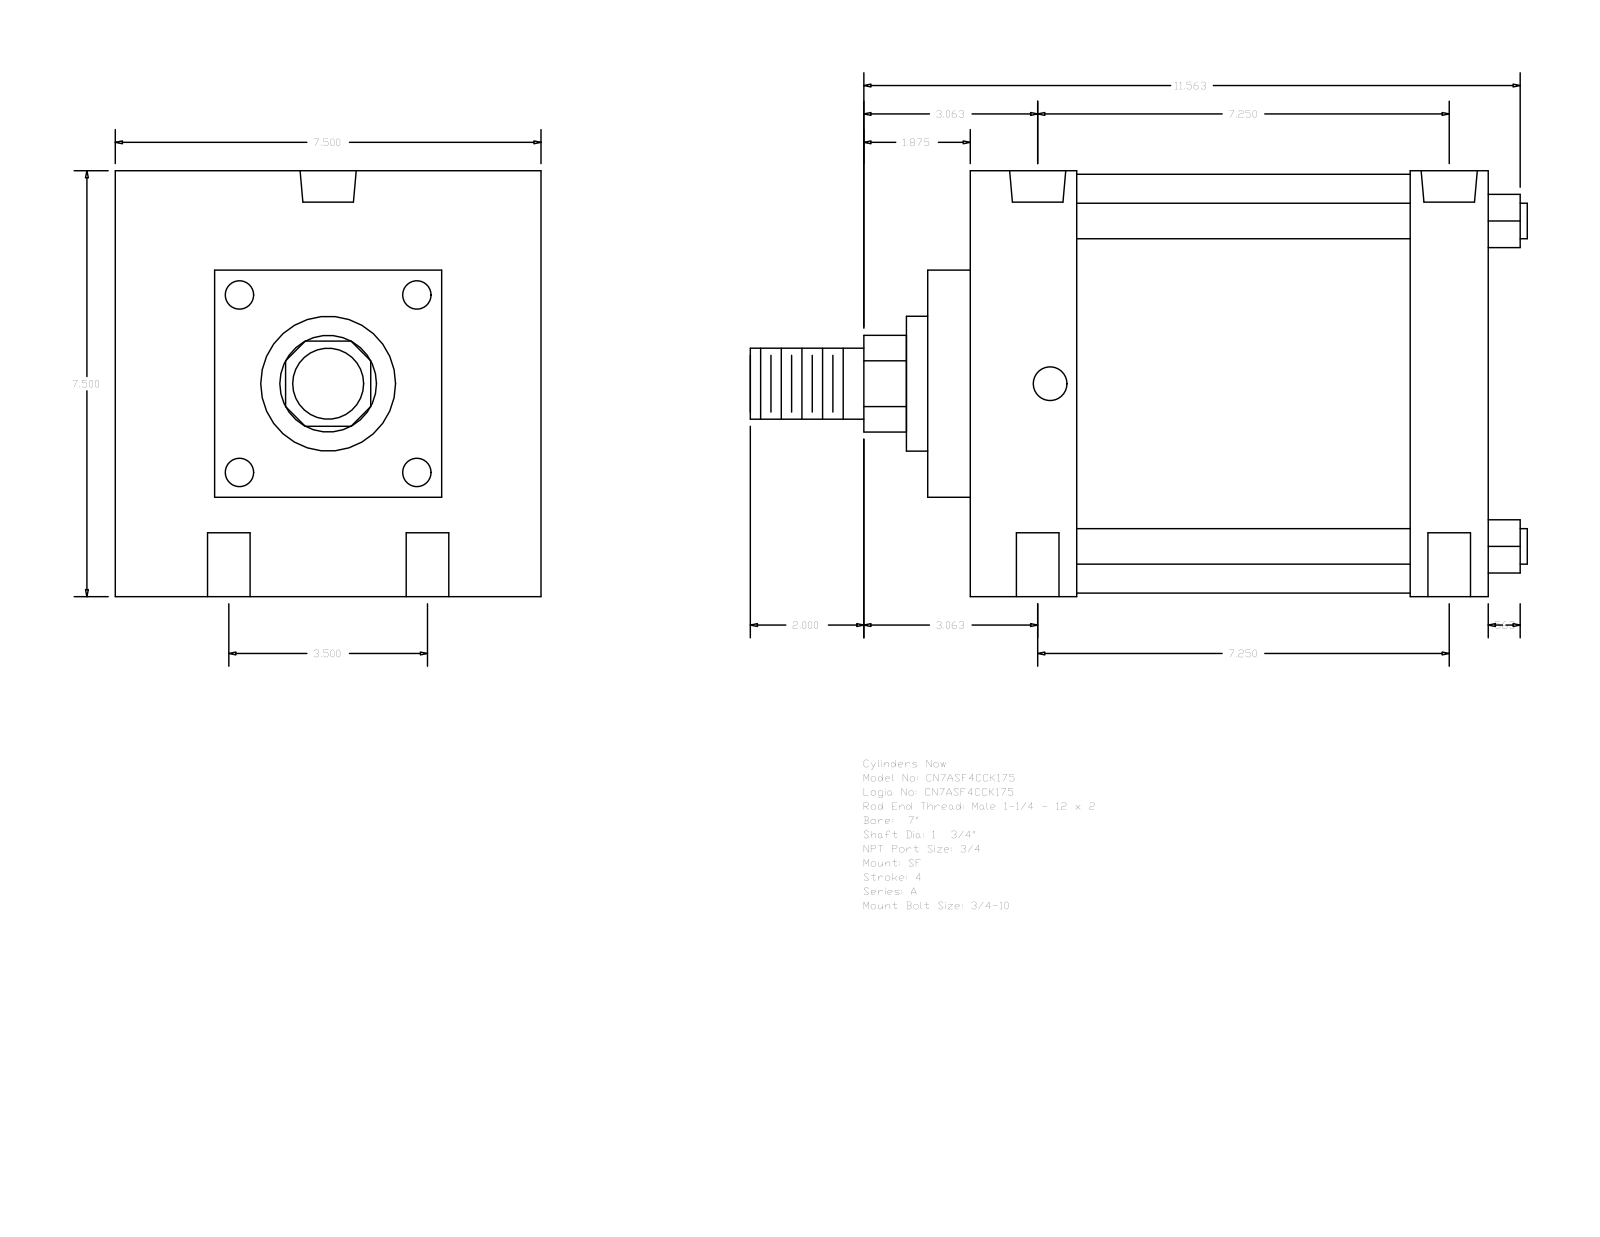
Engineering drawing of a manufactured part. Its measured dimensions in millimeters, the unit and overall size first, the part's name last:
Units: millimetres
Overall size (bounding box): 347.66 × 190.5 × 190.5
Round holes (diameter × count): ⌀19.05 ×4, ⌀15.08 ×2, ⌀25.12 ×2
Round bosses / shafts (diameter × count): ⌀15.88 ×4, ⌀187.32 ×1, ⌀60.33 ×1, ⌀44.45 ×1, ⌀31.75 ×1
Partial cylindrical surfaces — rounded edges, fillets, slot ends (radius × count): R21.63 ×1
Main face-to-face distances: 190.5, 231.78, 146.05, 19.05, 47.63, 196.85, 149.22, 184.15, 34.93, 44.45
Hole centre spacings: 44.45, 189.44, 184.15, 88.9, 204.49, 173.03
Bodies: 0 solids, 93 faces (67 planar, 26 cylindrical, 0 other)
Part name (STEP PRODUCT): A_SF__0700_1.75
STEP written by: GSSL Pune (CONFIG_CONTROL_DESIGN)
